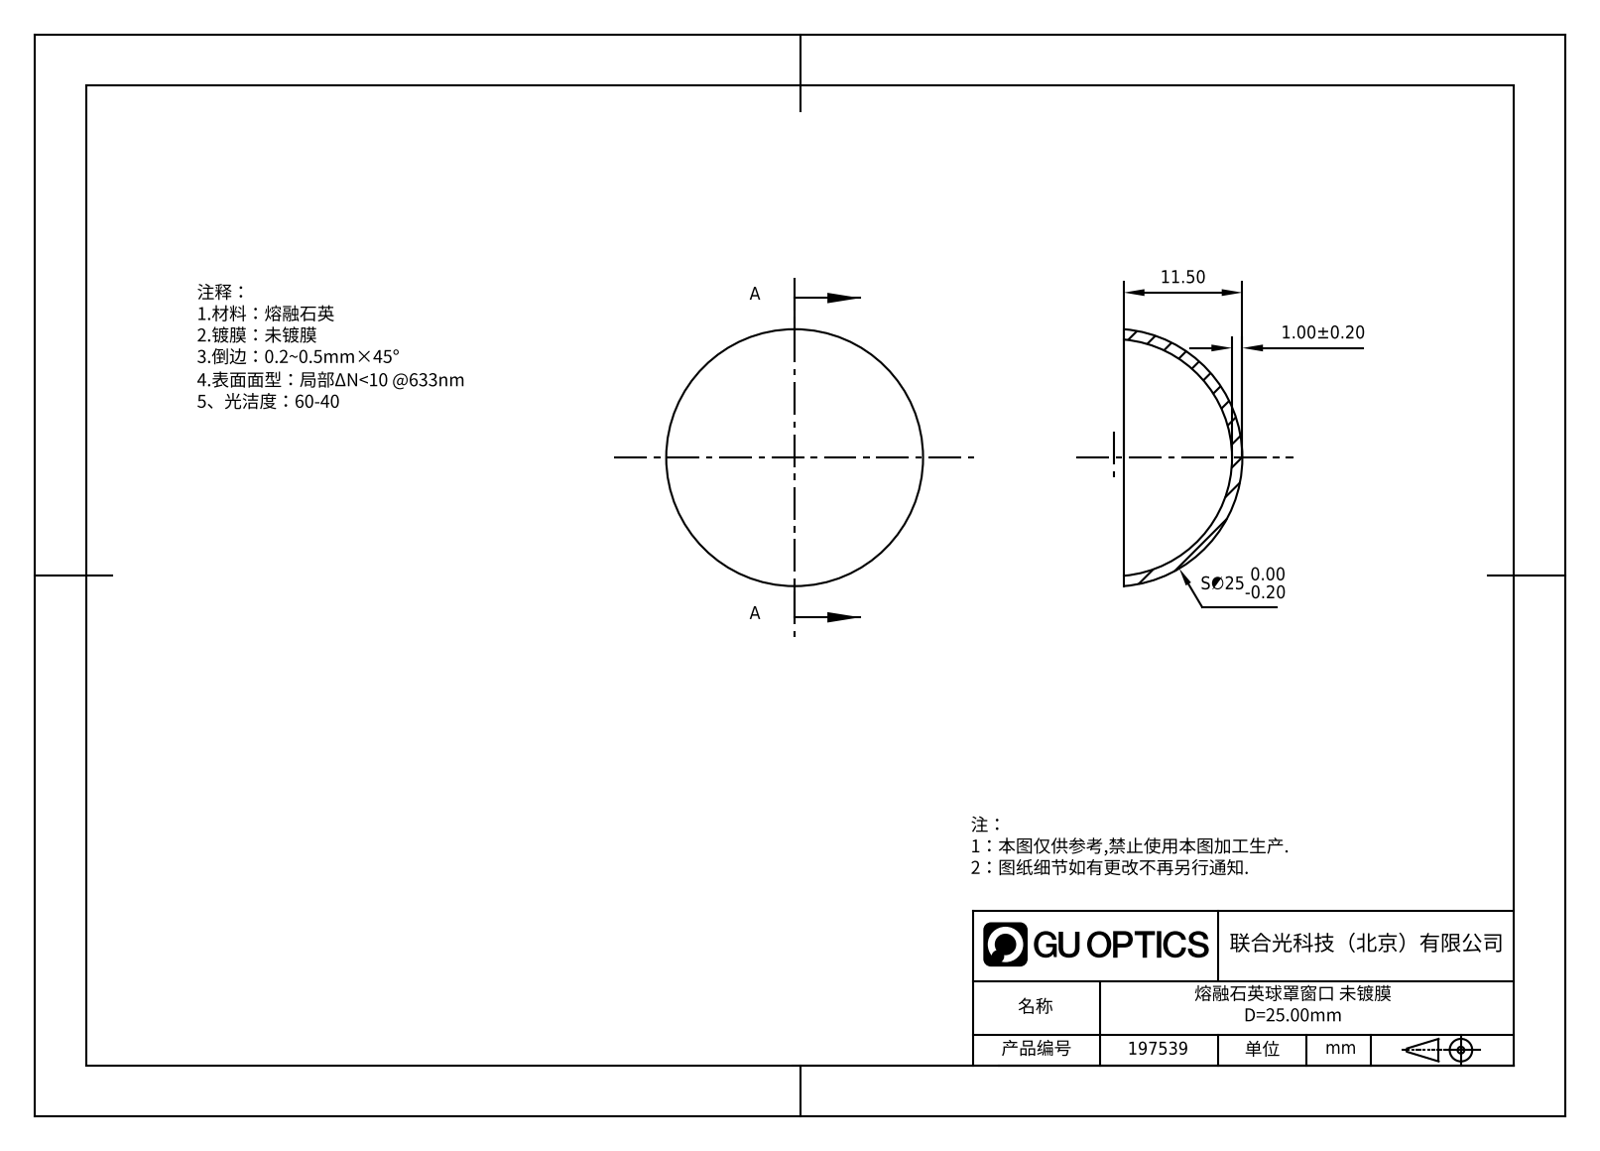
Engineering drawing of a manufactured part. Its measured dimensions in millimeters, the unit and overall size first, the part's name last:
Units: millimetres
Overall size (bounding box): 24.92 × 24.92 × 11.5
Volume: 830 mm³ · Surface area: 1 737 mm²
Bodies: 1 solid, 5 faces (1 planar, 0 cylindrical, 4 other)
Part name (STEP PRODUCT): 197539
STEP written by: SolidWorks 2016 (AUTOMOTIVE_DESIGN)
